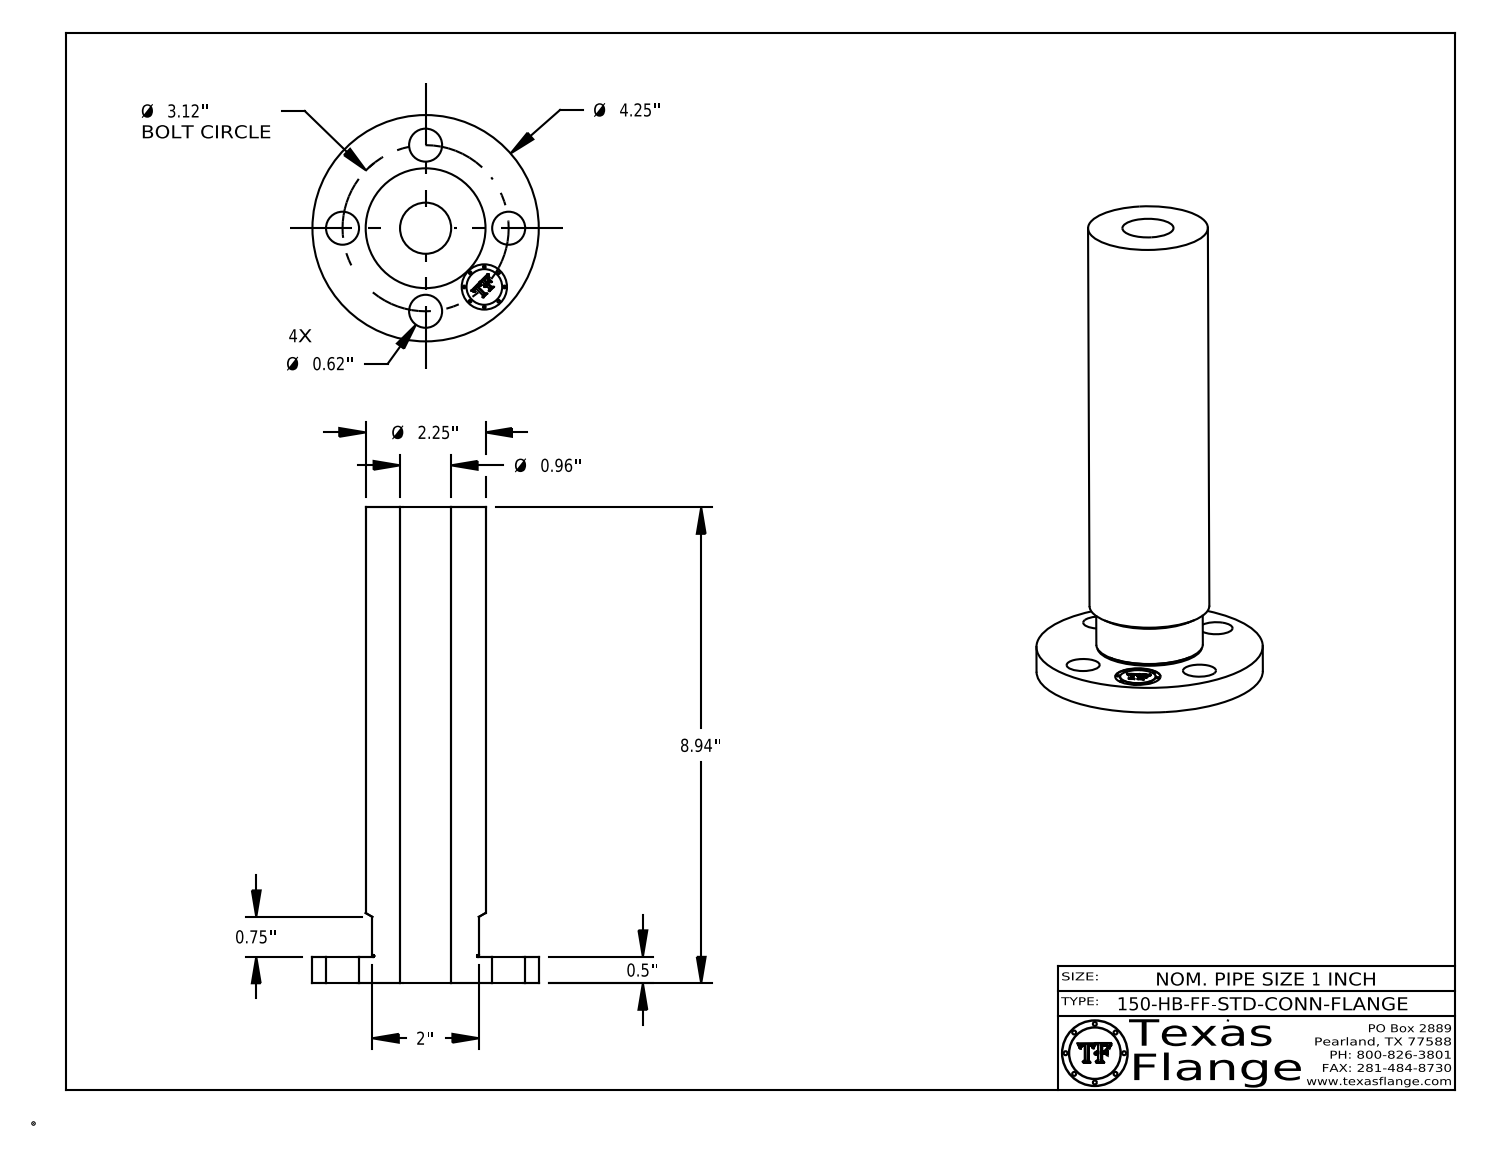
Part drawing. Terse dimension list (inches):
name: 1-150-HB-FF-STD-CONN-FLANGE
written by: CATIA V5 STEP AP214 (AUTOMOTIVE_DESIGN)
unit: in
bodies: 1 solid, 410 faces (368 planar, 36 cylindrical, 6 other)
size: 8.938 × 4.25 × 4.25
volume: 32.88 in³; area: 122.6 in²
holes: 4× ⌀0.62, 1× ⌀0.85, 1× ⌀0.96
bosses: 8× ⌀0.051, 1× ⌀4.25, 1× ⌀2.25, 1× ⌀2, 1× ⌀0.67
face distances: 0.498, 8.937, 8.44, 0.493, 8.445, 0.254, 0.248, 0.016, 0.046, 0.165
hole spacings: 1.56, 2.206, 1.194, 2.882, 3.12, 1.56
